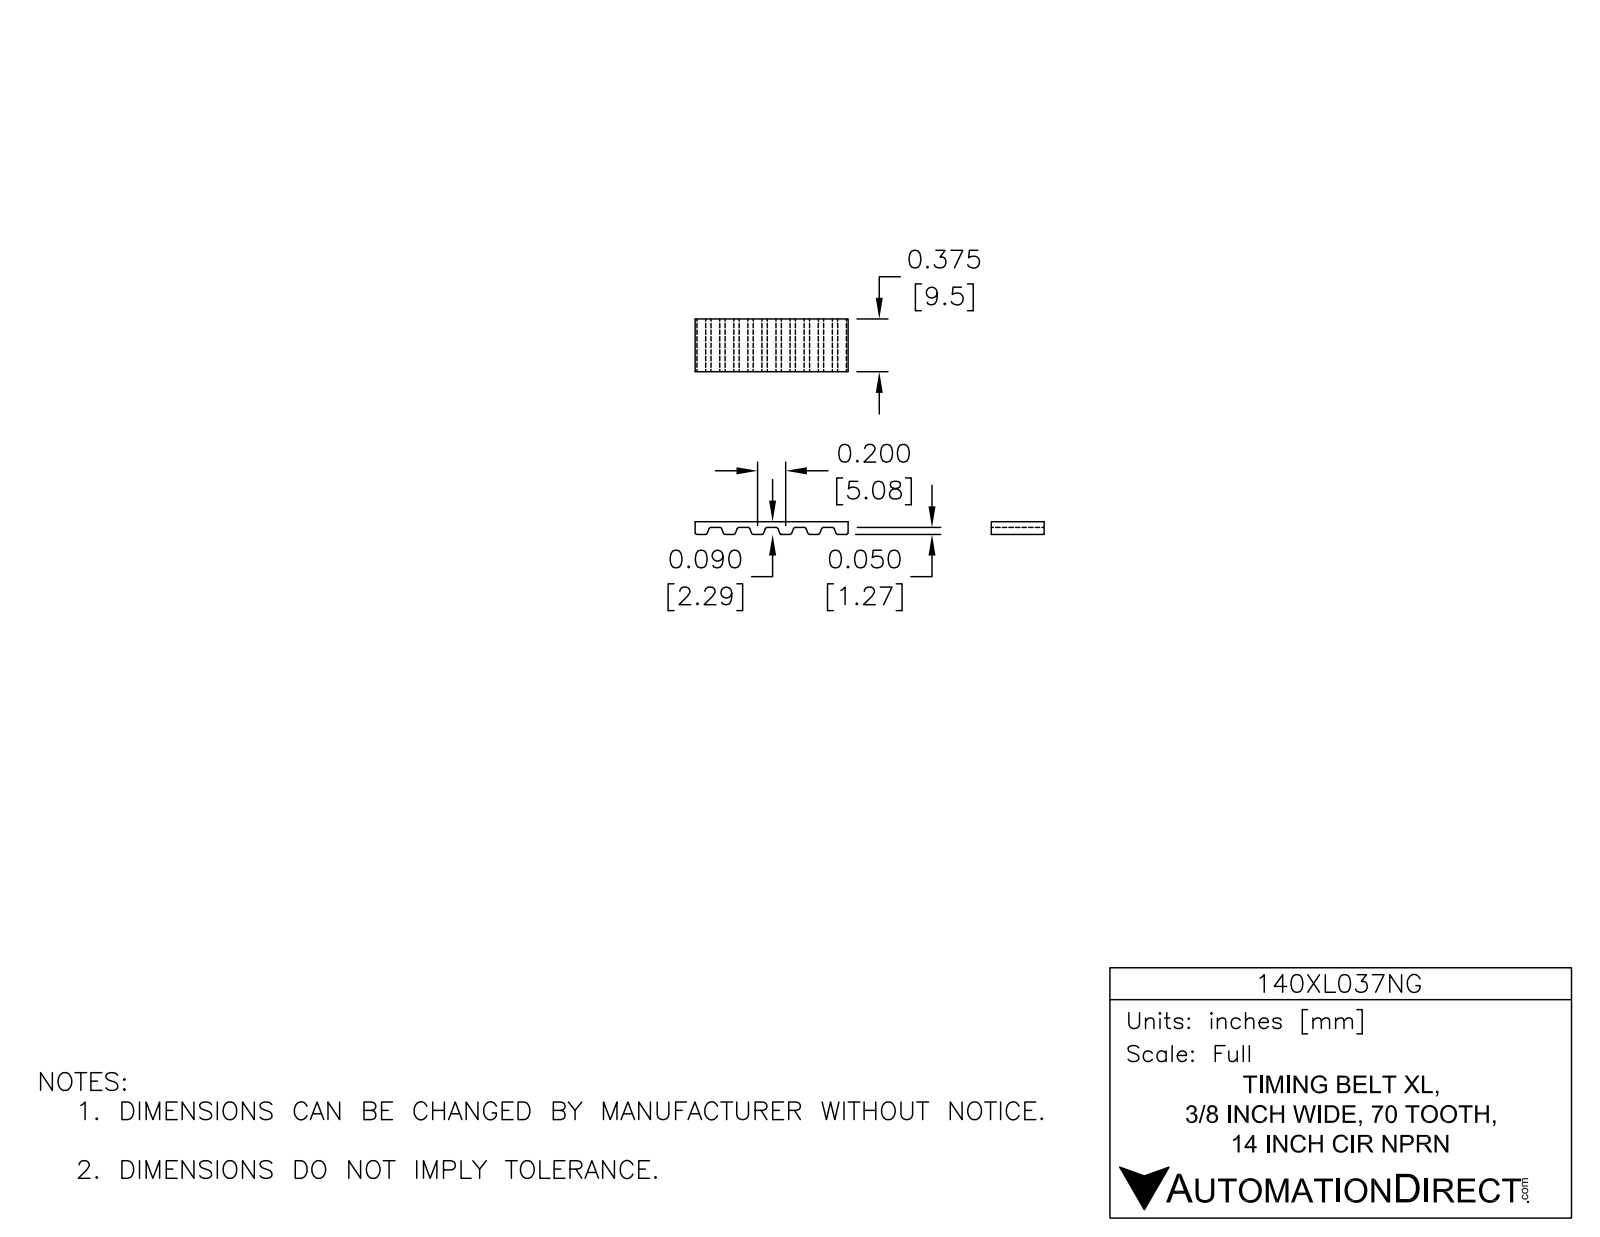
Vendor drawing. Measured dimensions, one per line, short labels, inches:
name: 140XL037NG
written by: SolidWorks 2014 (AUTOMOTIVE_DESIGN)
unit: in
bodies: 1 solid, 598 faces (238 planar, 360 cylindrical, 0 other)
size: 5.288 × 3 × 0.375
volume: 0.285 in³; area: 13.37 in²
rounds: 280× R0.015, 2× R1.46, 2× R1.5
face distances: 0.04, 2.96, 3, 0.375, 0.178, 2.92, 0.356, 0.534, 0.712, 0.89
